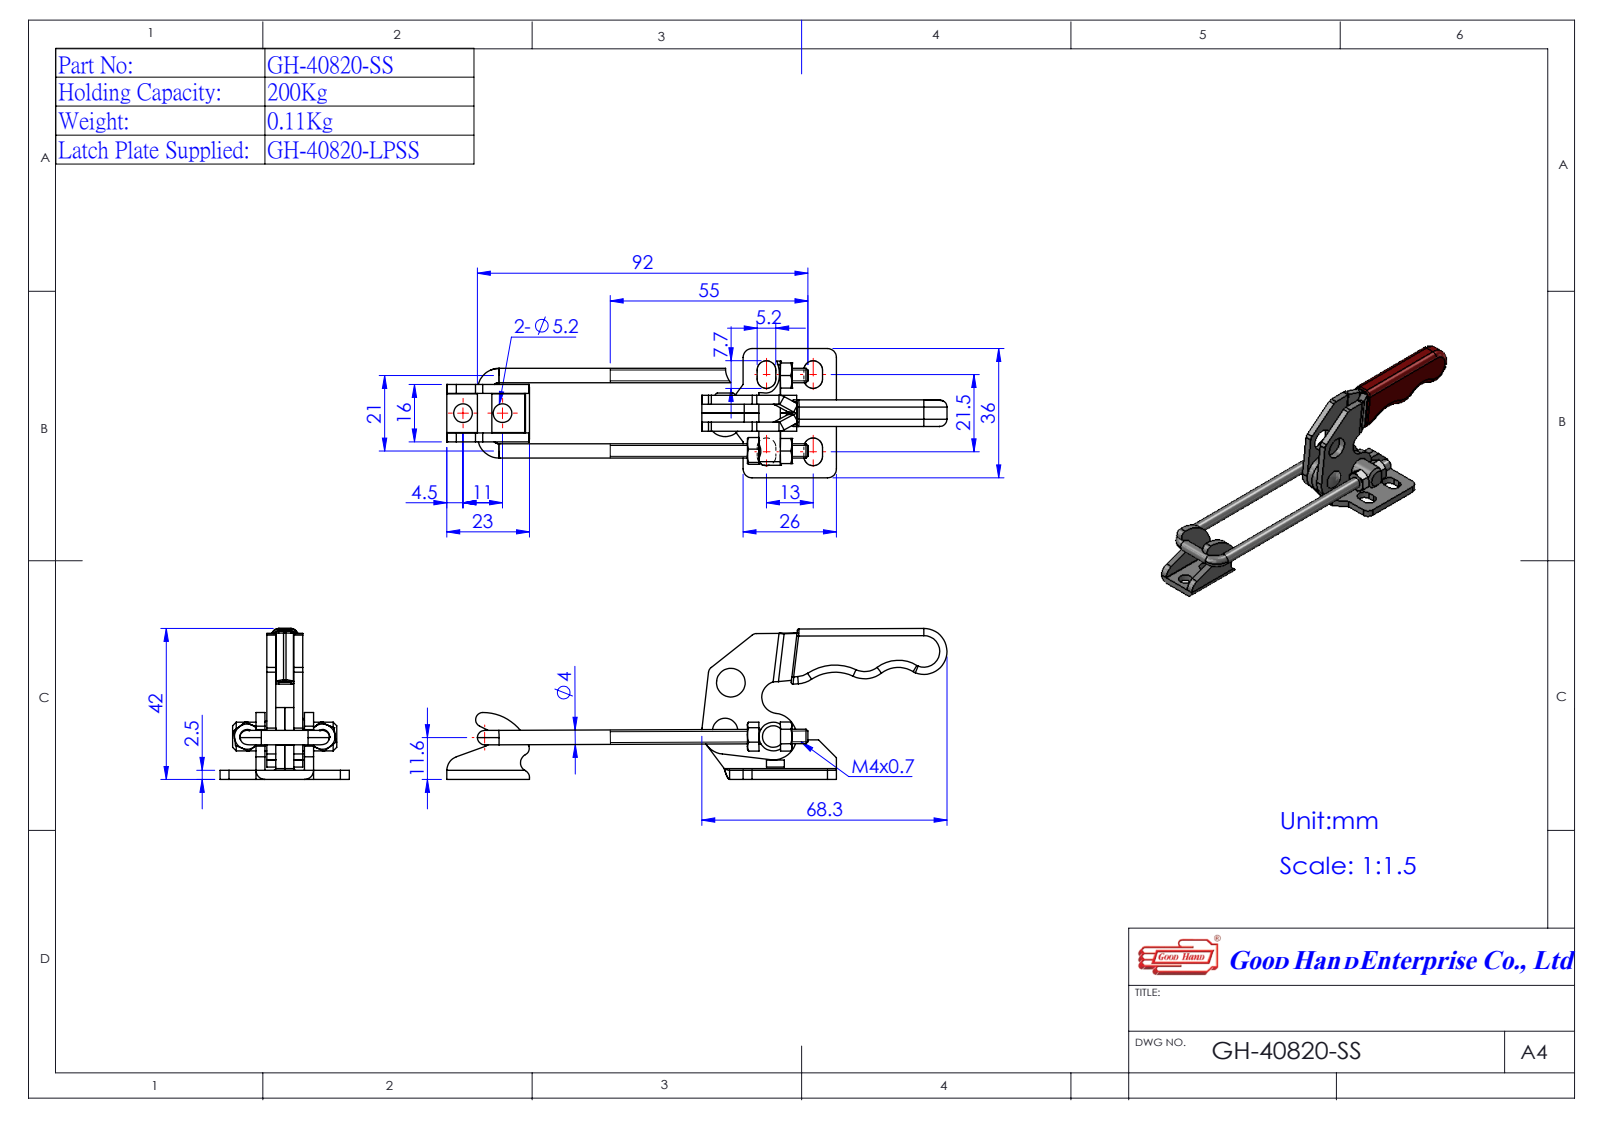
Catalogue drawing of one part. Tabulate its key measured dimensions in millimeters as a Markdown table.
| quantity | value |
| --- | --- |
| part name | Group3^GH-40820(簡化); Group1^GH-40820(簡化); 44082044-1^GH-40820(簡化); 14082015-1-1^GH-40820(簡化) (+2 more) |
| STEP written by | SolidWorks 2016 (AUTOMOTIVE_DESIGN) |
| units | millimeters |
| bodies | 7 solids, 287 faces (111 planar, 110 cylindrical, 66 other) |
| overall size | 139.25 × 42 × 36 |
| volume | 16 421 mm³ |
| surface area | 13 890 mm² |
| round holes (diameter × count) | 4 × 2, 8 × 2, 3 × 1 |
| round bosses / shafts (diameter × count) | 4 × 4 |
| partial cylindrical surfaces (radius × count) | 2 × 9, 2.5 × 9, 0.5 × 8, 2.6 × 8, 3 × 6, 4.5 × 4, 0.1 × 2, 6.5 × 2 |
| main face-to-face distances | 2.5, 7.5, 10.5, 5, 3, 10, 13, 0.5, 5.5, 13.5 |
| hole center spacings | 13.49, 13.5, 19.09, 21 |
